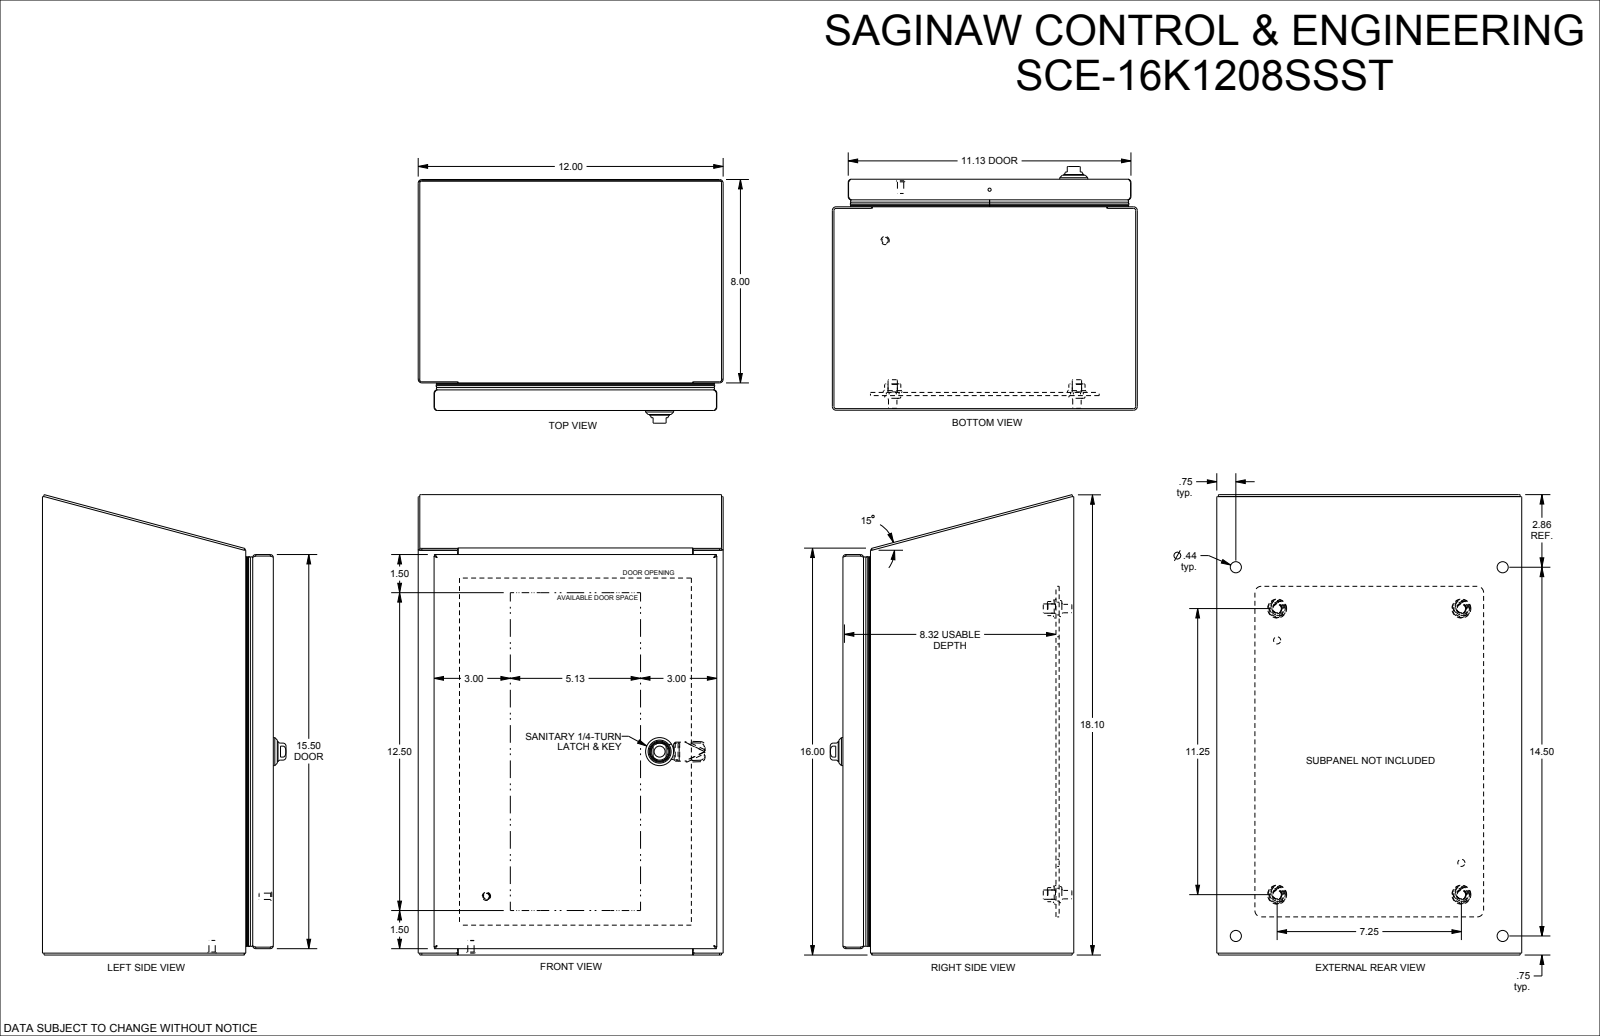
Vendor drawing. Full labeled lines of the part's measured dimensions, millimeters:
Part name (STEP PRODUCT): SCE-16K1208SSST
STEP written by: SolidWorks 2021 (AUTOMOTIVE_DESIGN)
Units: millimetres
Bodies: 39 solids, 2268 faces (785 planar, 586 cylindrical, 897 other)
Overall size (bounding box): 459.9 × 304.8 × 243.4
Volume: 1 832 000 mm³ · Surface area: 1 682 000 mm²
Round holes (diameter × count): ⌀4 ×4, ⌀5.1 ×4, ⌀9.3 ×4, ⌀11.1 ×4, ⌀12.7 ×4, ⌀6.4 ×2, ⌀6.8 ×2, ⌀7.1 ×2, ⌀10.4 ×2, ⌀5 ×1, ⌀5.2 ×1, ⌀8 ×1
Round bosses / shafts (diameter × count): ⌀9.3 ×4, ⌀8.4 ×4, ⌀6.3 ×4, ⌀4 ×4, ⌀5 ×3, ⌀14.3 ×2, ⌀28 ×1, ⌀23 ×1
Partial cylindrical surfaces — rounded edges, fillets, slot ends (radius × count): R0.8 ×64, R0.3 ×28, R6.4 ×20, R0.5 ×16, R1.3 ×16, R1.8 ×14, R0.7 ×12, R1.6 ×12
Main face-to-face distances: 1.9, 302.9, 1.5, 229.2, 227.3, 230.7, 228.8, 304.8, 301, 12.7
Hole centre spacings: 44.9, 229.2, 397.2, 241.3, 25, 31.7, 31.8, 52.2
